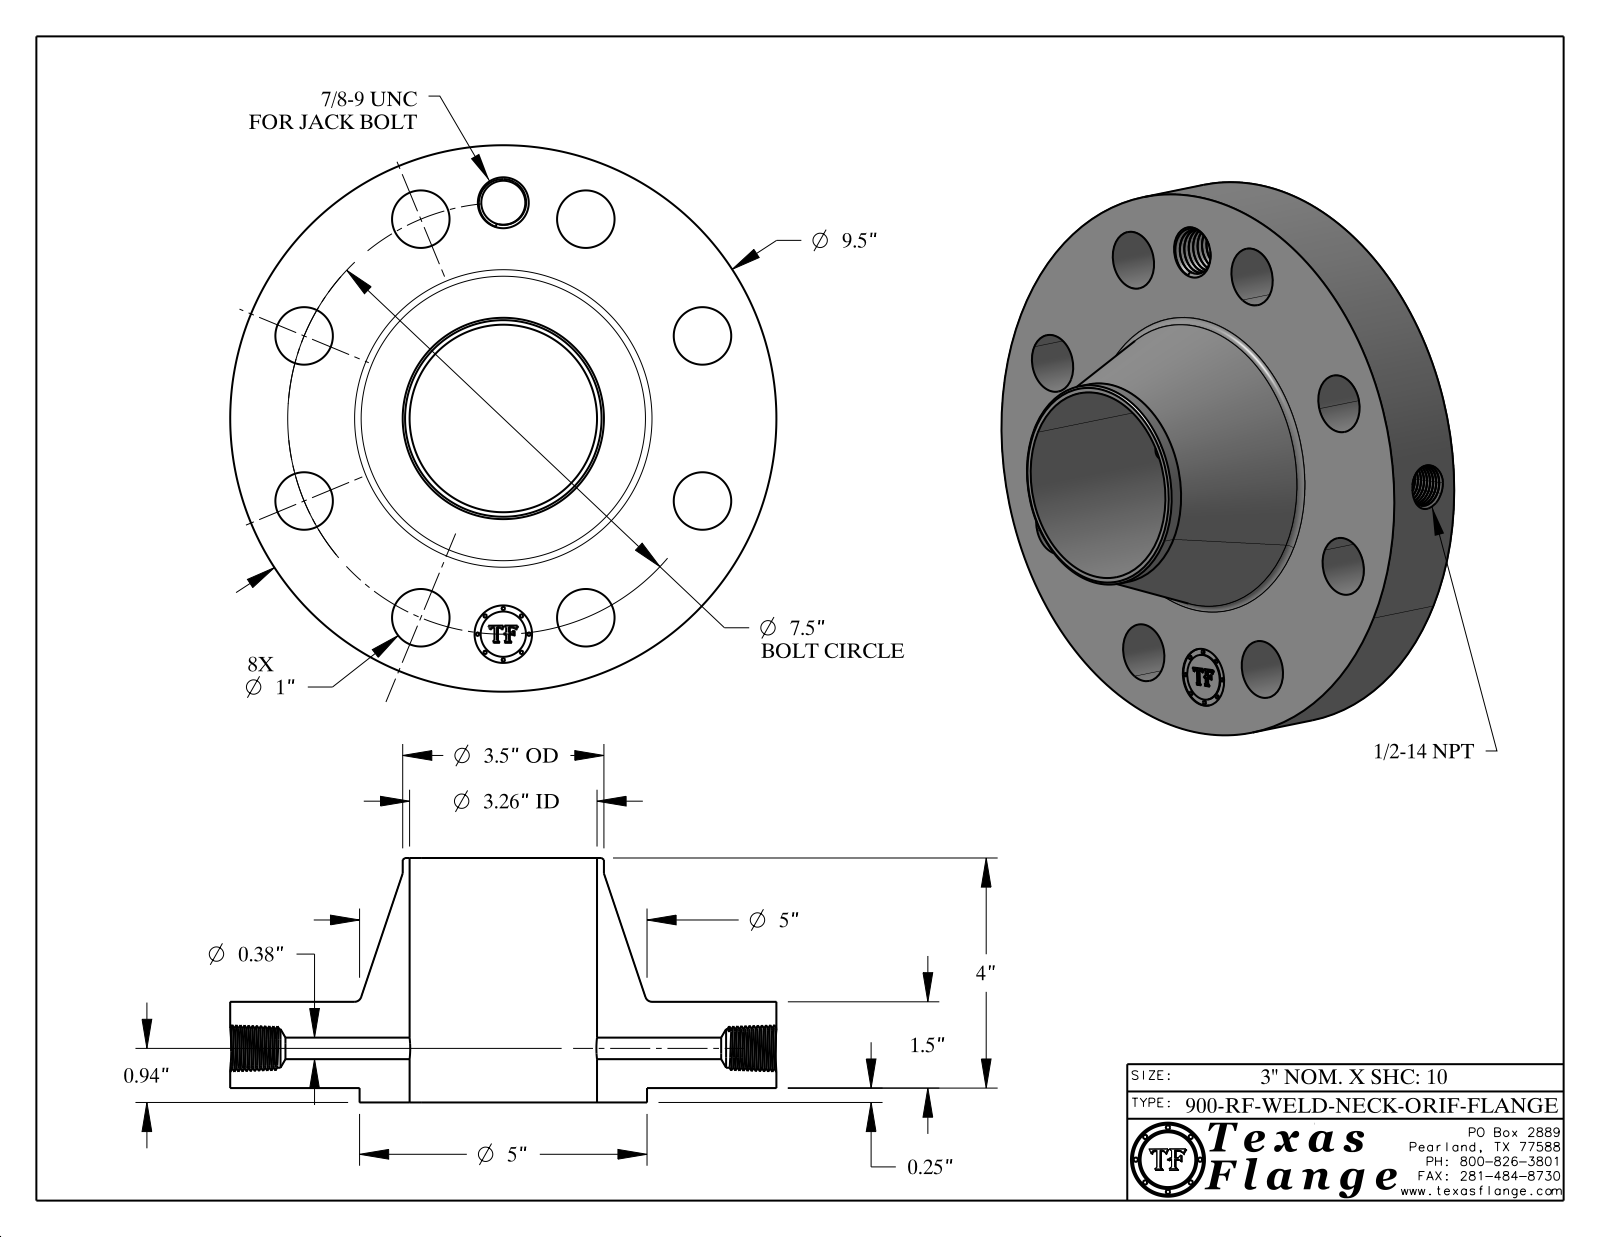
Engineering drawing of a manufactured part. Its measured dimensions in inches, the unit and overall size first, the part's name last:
Units: inches
Overall size (bounding box): 9.5 × 9.5 × 4.25
Round holes (diameter × count): ⌀1 ×9, ⌀0.375 ×1, ⌀0.672 ×1, ⌀0.766 ×1, ⌀3.26 ×1
Round bosses / shafts (diameter × count): ⌀0.061 ×8, ⌀9.5 ×1, ⌀5 ×1, ⌀3.5 ×1, ⌀0.788 ×1
Main face-to-face distances: 1.5, 0.25, 1.75, 4.25, 4, 2.5, 1.735, 1.485, 0.015, 2.515
Hole centre spacings: 3.75, 2.87, 5.303, 6.929, 7.5, 1.463, 4.167, 6.236
Volume: 98.87 in³ · Surface area: 282.4 in²
Bodies: 1 solid, 759 faces (369 planar, 90 cylindrical, 300 other)
Part name (STEP PRODUCT): 900-RF-WELD-NECK
STEP written by: CATIA V5 STEP AP214 (AUTOMOTIVE_DESIGN)
